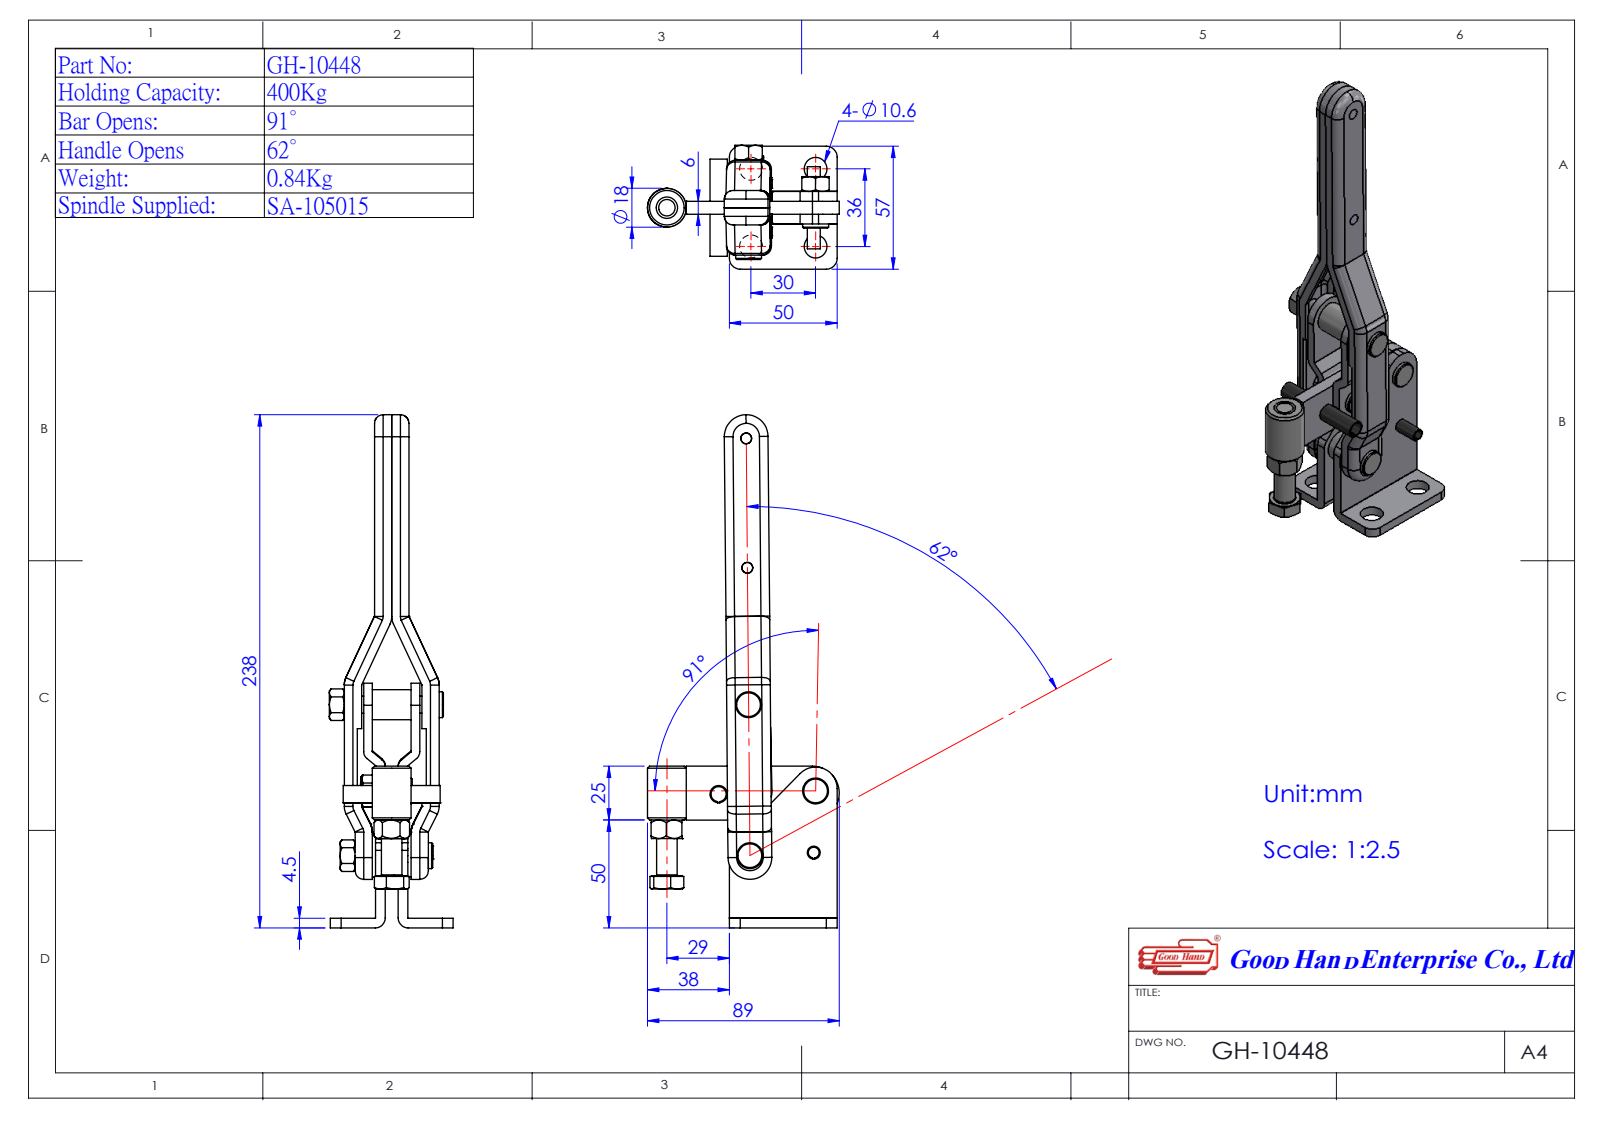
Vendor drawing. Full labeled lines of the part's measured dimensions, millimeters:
Part name (STEP PRODUCT): GH-10448(簡化)-1; Group4^GH-10448(簡化)-1; Group2^GH-10448(簡化)-1; Group5^GH-10448(簡化)-1 (+2 more)
STEP written by: SolidWorks 2016 (AUTOMOTIVE_DESIGN)
Units: millimetres
Bodies: 6 solids, 556 faces (261 planar, 179 cylindrical, 116 other)
Overall size (bounding box): 238.01 × 89.25 × 57.43
Volume: 99 045 mm³ · Surface area: 67 479 mm²
Round holes (diameter × count): ⌀10.6 ×4, ⌀6 ×3, ⌀5 ×1, ⌀7 ×1, ⌀7.94 ×1
Round bosses / shafts (diameter × count): ⌀9 ×4, ⌀6 ×3, ⌀20 ×1, ⌀18 ×1, ⌀12 ×1, ⌀10 ×1, ⌀8 ×1
Partial cylindrical surfaces — rounded edges, fillets, slot ends (radius × count): R2 ×20, R4 ×20, R0.1 ×14, R8.1 ×8, R5 ×5, R2.1 ×4, R4.1 ×4, R6.1 ×4
Main face-to-face distances: 2, 4.5, 6, 10.5, 15, 14, 12, 16, 1.5, 3
Hole centre spacings: 30, 36, 42.95, 46.86, 71.31, 14.88, 28.61, 30.2
